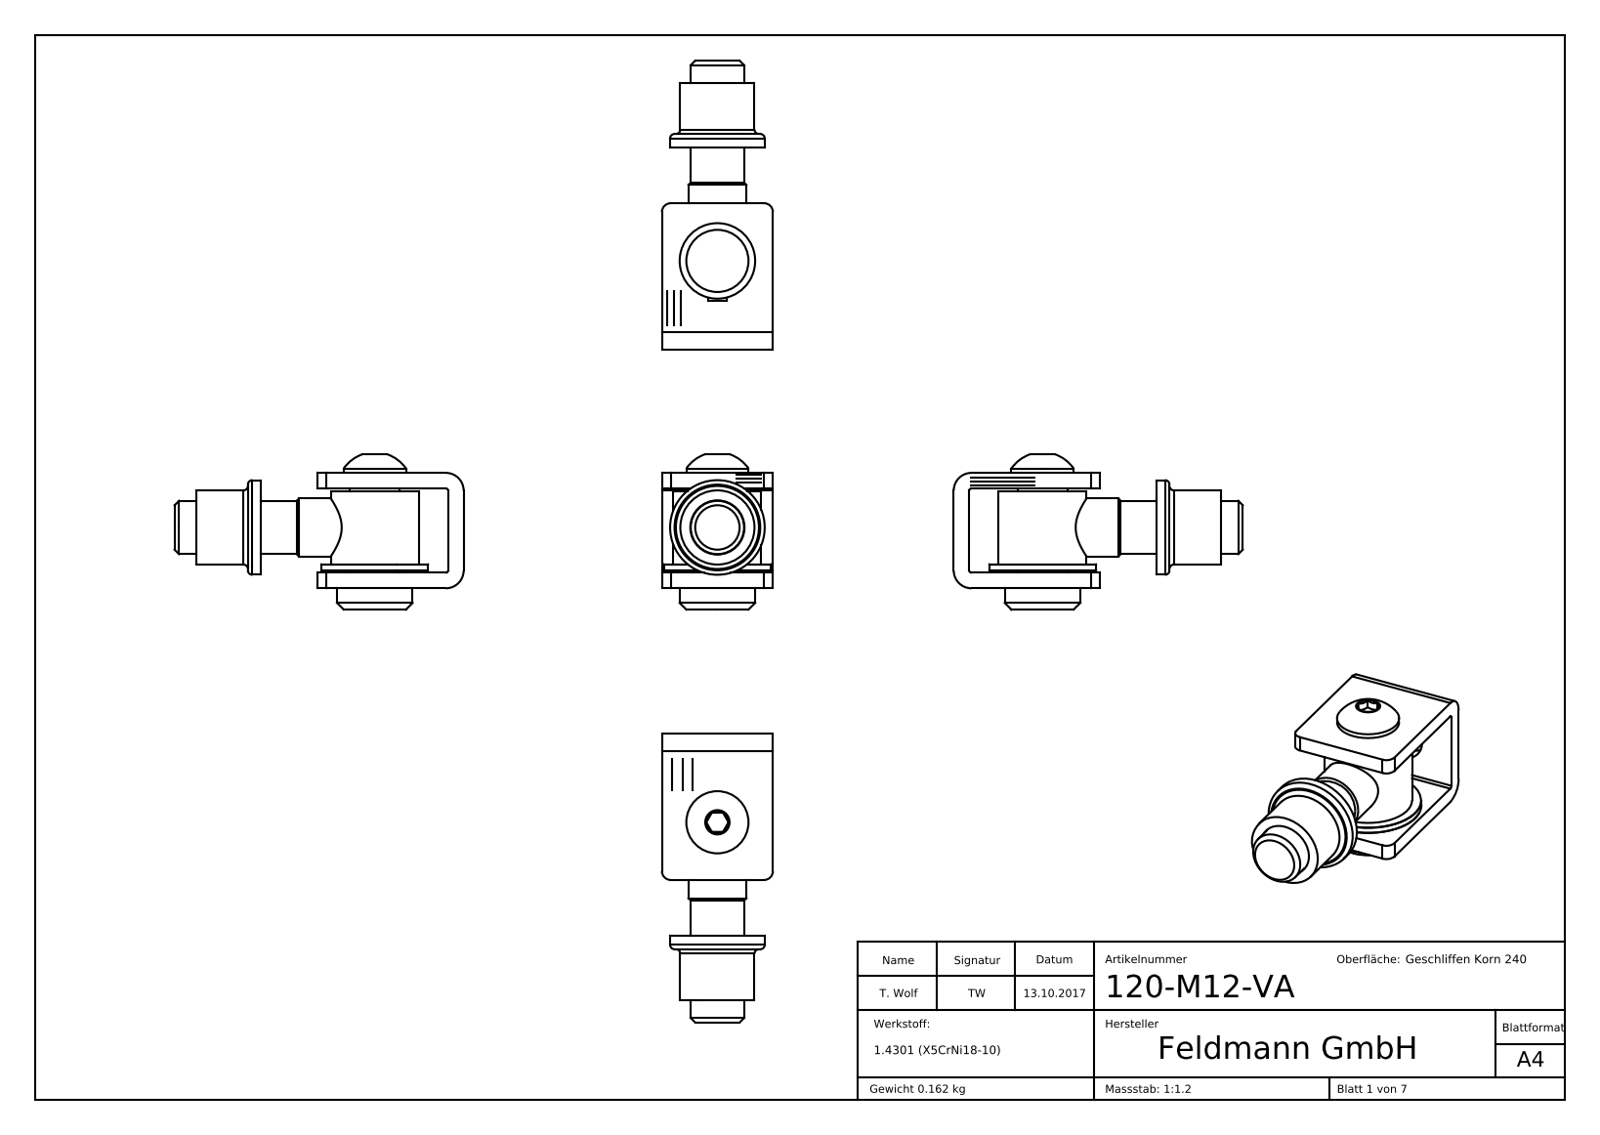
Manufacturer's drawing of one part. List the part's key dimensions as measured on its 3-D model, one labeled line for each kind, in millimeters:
Part name (STEP PRODUCT): ISO7380 - M6x16_ISO7380 - M6x16; 120-M12-VA Teil2_120-M12-VA Teil 2; 120-M12-VA Teil1_120-M12-VA Teil 1; 120-M12-VA Teil5_120-M12-VA Teil5 Keyshot (+3 more)
STEP written by: SolidWorks 2015 (CONFIG_CONTROL_DESIGN)
Units: millimetres
Bodies: 6 solids, 331 faces (176 planar, 45 cylindrical, 110 other)
Overall size (bounding box): 65.1 × 35 × 25
Volume: 20 516 mm³ · Surface area: 13 174 mm²
Round holes (diameter × count): ⌀5 ×1, ⌀7.55 ×1, ⌀10 ×1, ⌀10.2 ×1, ⌀11.9 ×1, ⌀12 ×1, ⌀13 ×1
Round bosses / shafts (diameter × count): ⌀24 ×1, ⌀21.3 ×1, ⌀19.8 ×1, ⌀17 ×1, ⌀16.7 ×1, ⌀14 ×1, ⌀13 ×1, ⌀12 ×1
Partial cylindrical surfaces — rounded edges, fillets, slot ends (radius × count): R0.5 ×2, R2 ×2, R4 ×2
Main face-to-face distances: 3.5, 22.5, 26, 19, 0.55, 4.05, 20.55, 21.95, 17.05, 18.45
Hole centre spacings: 0.7
